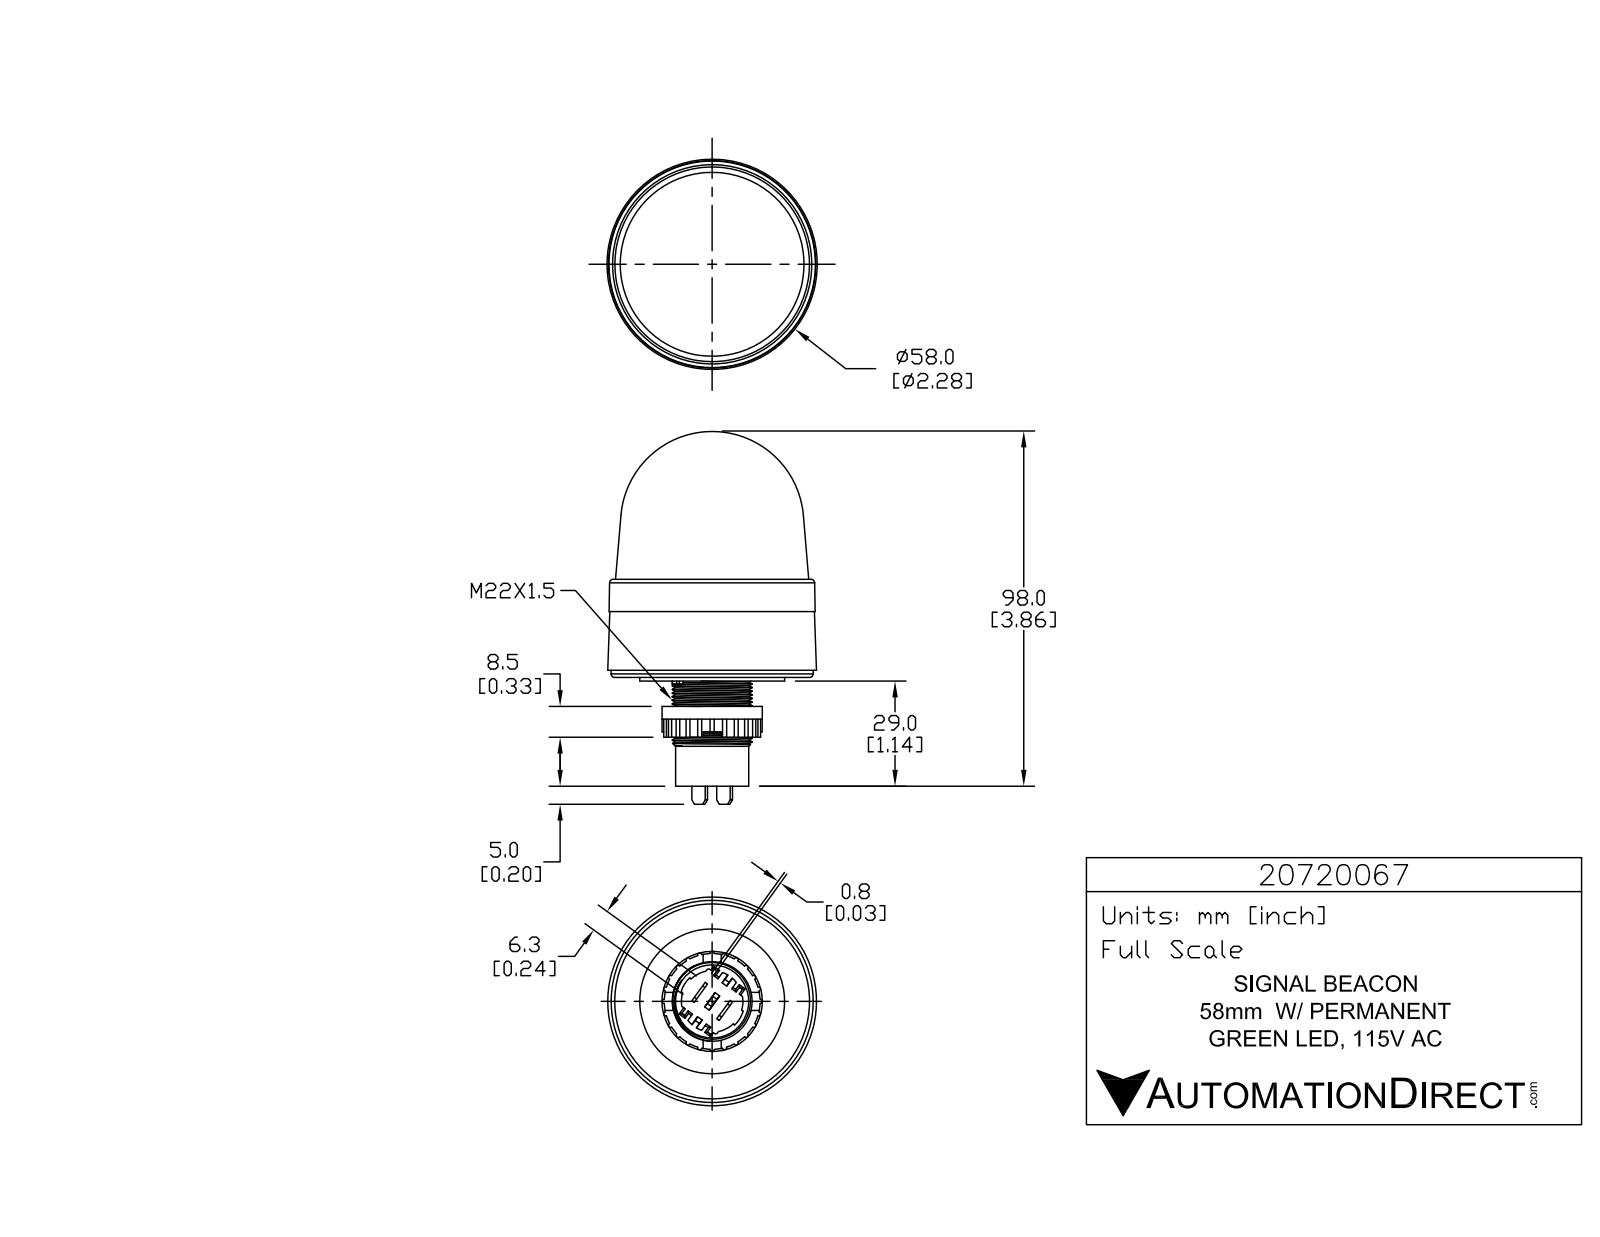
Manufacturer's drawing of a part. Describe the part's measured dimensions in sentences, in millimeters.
The part is named "20720067". Its 3-D file was written by "SolidWorks 2015 (AUTOMOTIVE_DESIGN)". It is 1 solid with 266 faces: 119 planar, 120 cylindrical and 27 other. Overall it measures 102.9 by 57.6 by 57.6 millimeters. Its volume is 147 700 cubic millimeters and its surface area 20 030 square millimeters. Round holes: 1 of diameter 23. Round bosses or shafts: 1 of diameter 55.8, 1 of diameter 40, 1 of diameter 27.7, 1 of diameter 22, 1 of diameter 20.2. Partial cylindrical surfaces (rounded edges, fillets, slot ends): 24 of radius 0.6, 2 of radius 0.5, 1 of radius 8.5, 1 of radius 9, 1 of radius 13.3. The main face-to-face distances are 1, 7, 3, 29, 8.5, 8, 27, 19, 26, 18.5.
